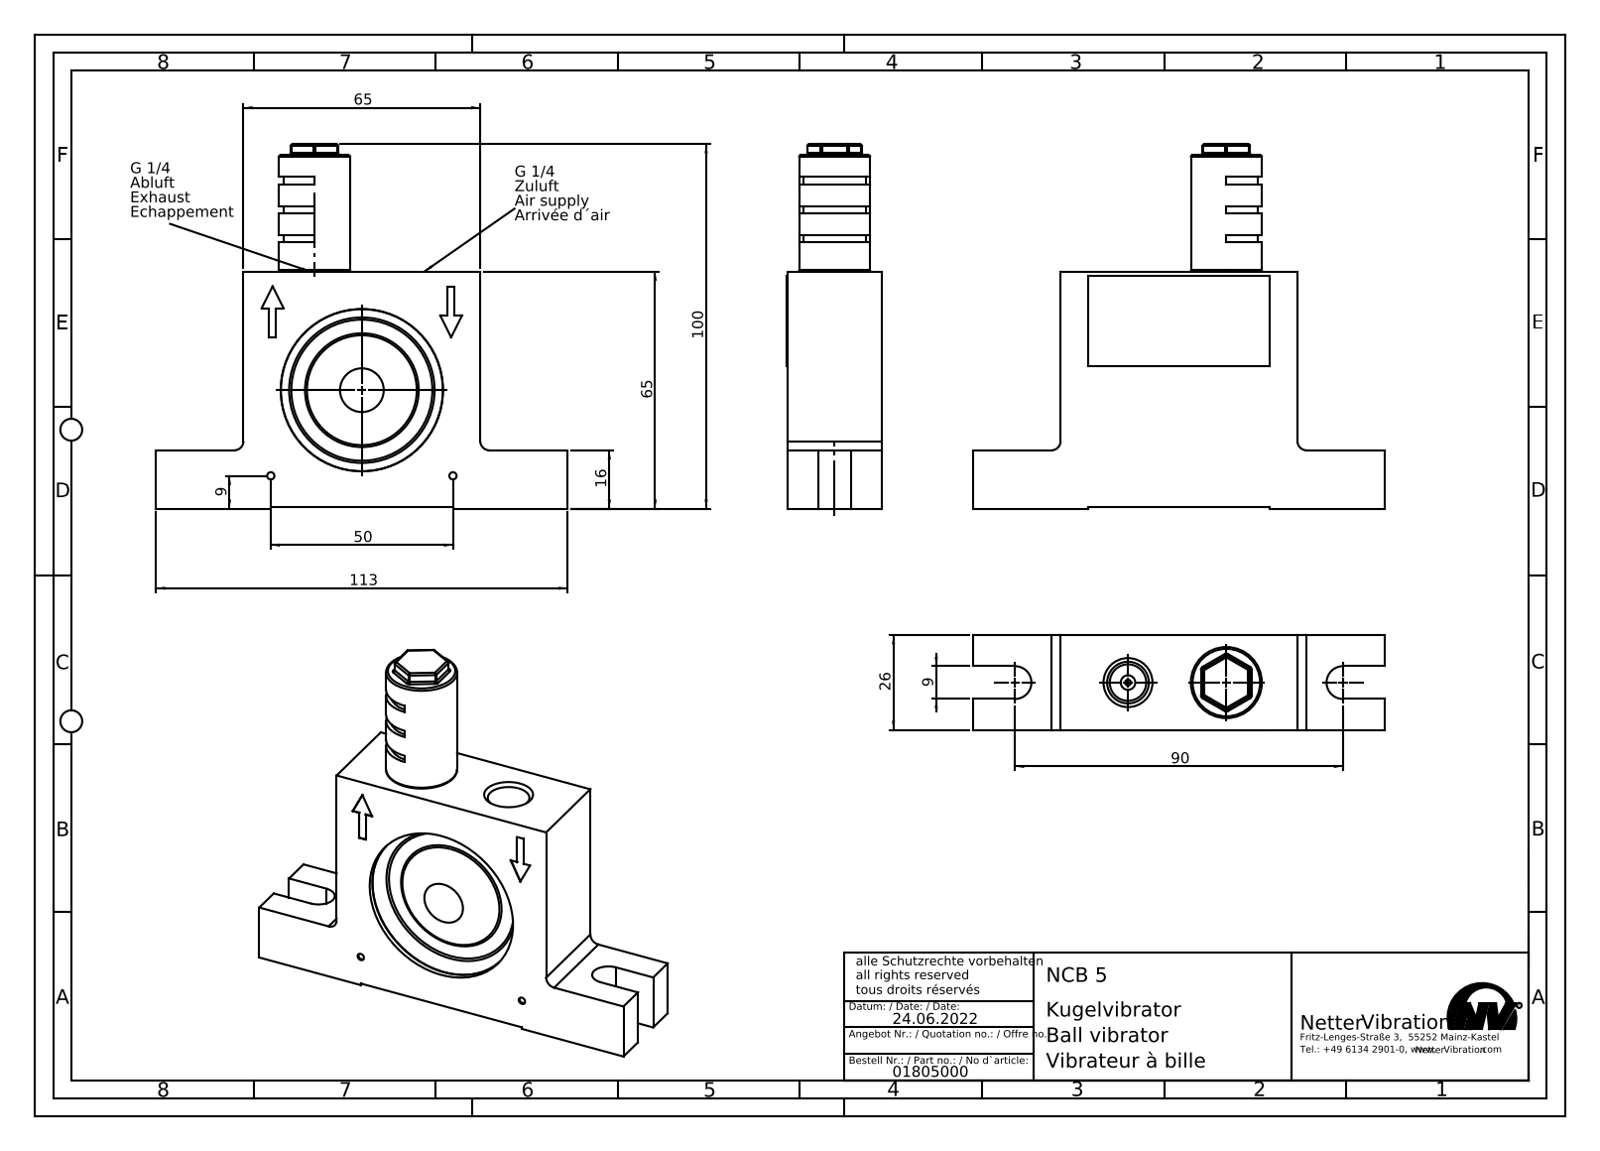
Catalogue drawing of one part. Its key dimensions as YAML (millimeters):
part_name: "NCB 5 Kugelvibrator #01805000"
step_written_by: "SolidWorks 2015 (AUTOMOTIVE_DESIGN)"
units: millimeters
bodies: {solids: 3, faces: 220, planar: 102, cylindrical: 49, other: 69}
overall_size: [113, 100, 26]
volume: 123071
surface_area: 28617
round_holes:
  - {diameter: 2, count: 2}
  - {diameter: 10, count: 2}
  - {diameter: 11.45, count: 2}
  - {diameter: 42, count: 1}
  - {diameter: 44.5, count: 1}
round_bosses_or_shafts:
  - {diameter: 19.5, count: 1}
  - {diameter: 13.16, count: 1}
partial_cylinders:
  - {radius: 0.5, count: 18}
  - {radius: 2.5, count: 2}
  - {radius: 4.5, count: 2}
  - {radius: 8.5, count: 1}
face_to_face_distances: [26, 65, 19, 7, 0.5, 64.5, 16, 49, 15.5, 8.5]
hole_center_spacings: [34.31, 27, 50]
